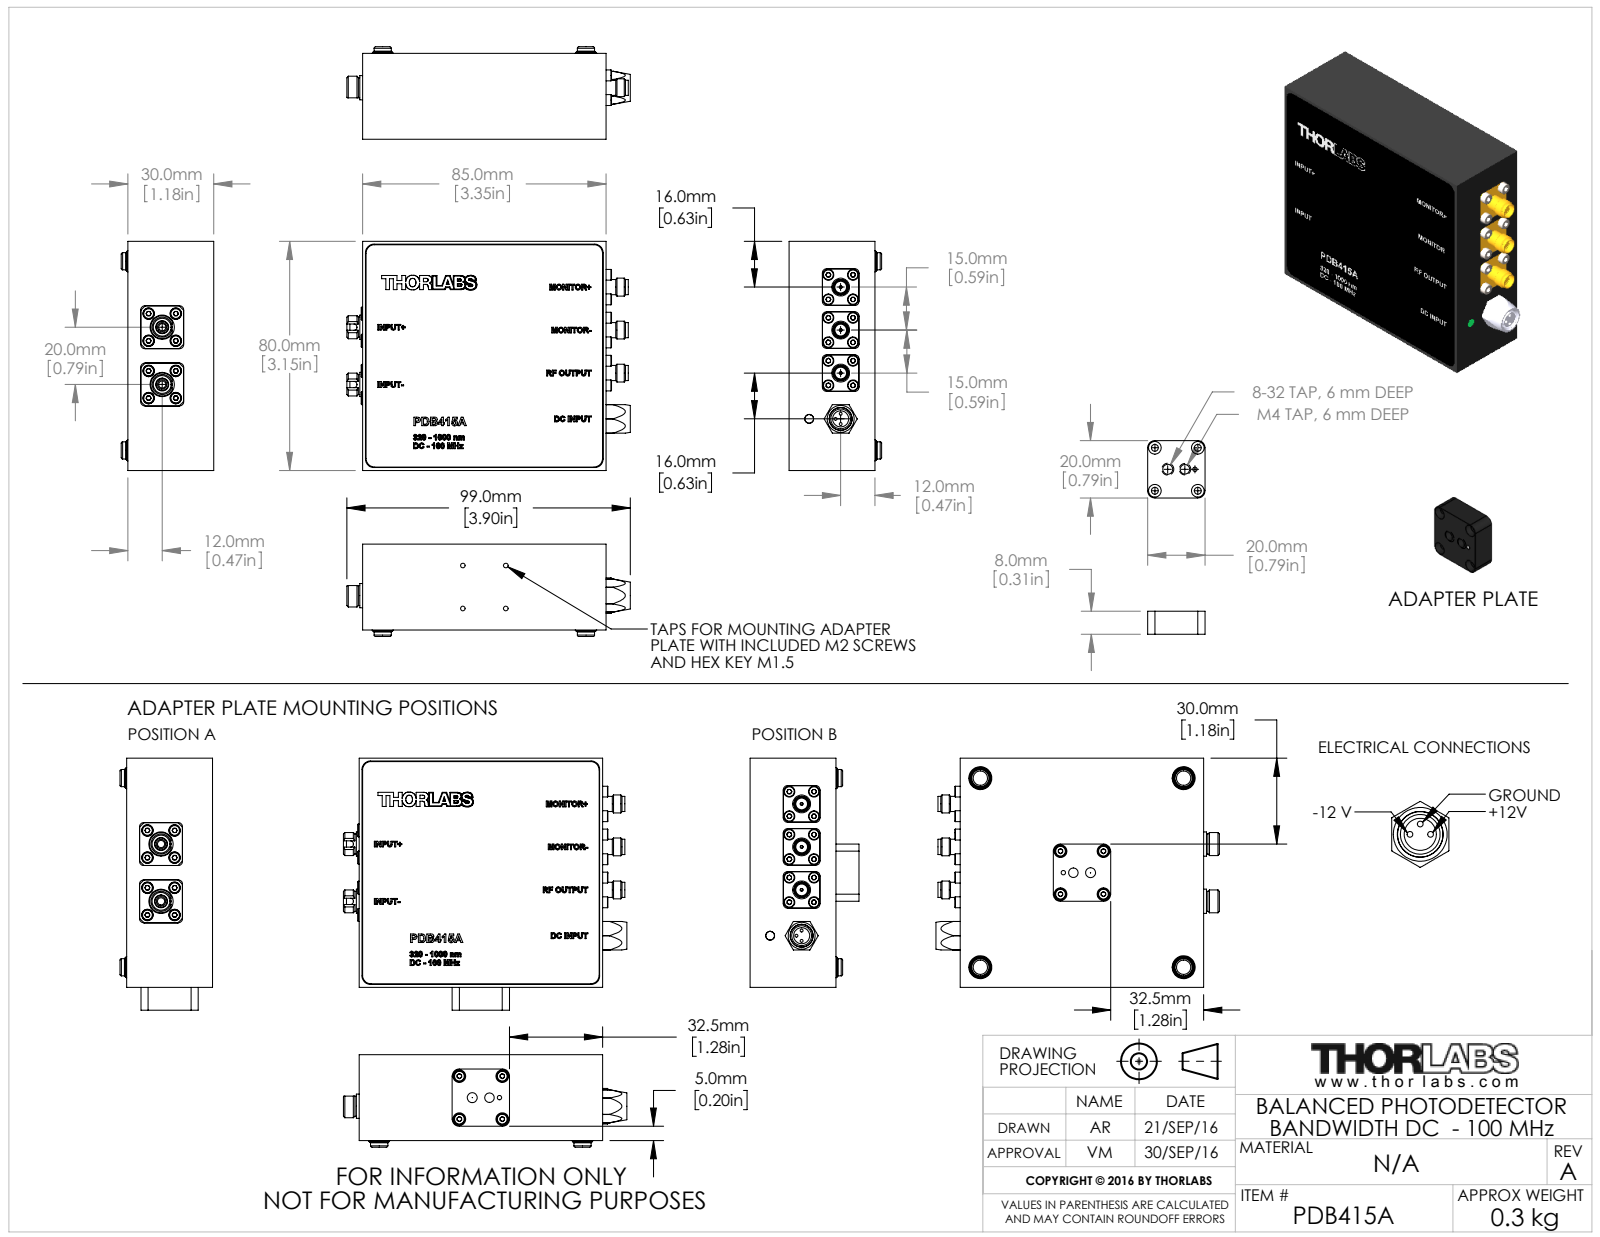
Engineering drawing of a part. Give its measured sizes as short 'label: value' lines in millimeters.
name: MTN005471-E0W
written by: SolidWorks 2016 (AUTOMOTIVE_DESIGN)
unit: mm
bodies: 95 solids, 3174 faces (1829 planar, 624 cylindrical, 721 other)
size: 99 × 88 × 38
volume: 112 014 mm³; area: 71 717 mm²
holes: 38× ⌀1.6, 12× ⌀2.4, 12× ⌀2.6, 12× ⌀4.4, 8× ⌀2.2, 8× ⌀4, 6× ⌀1.02, 5× ⌀8, 3× ⌀0.8, 3× ⌀1, 3× ⌀4.1, 3× ⌀4.2
bosses: 24× ⌀3.8, 24× ⌀2, 8× ⌀4.5, 8× ⌀2.5, 6× ⌀0.43, 4× ⌀6, 3× ⌀6.22, 3× ⌀5.3
rounds: 20× R1.5, 16× R3, 8× R2.5, 8× R5, 4× R1, 4× R2.4, 2× R9.5, 1× R5.75
face distances: 4.2, 29.9, 25.7, 4, 29.7, 6, 19.7, 23.7, 23.9, 5.5
hole spacings: 15, 6.08, 8.6, 9.5, 6.72, 8.75, 11.53, 12.9
